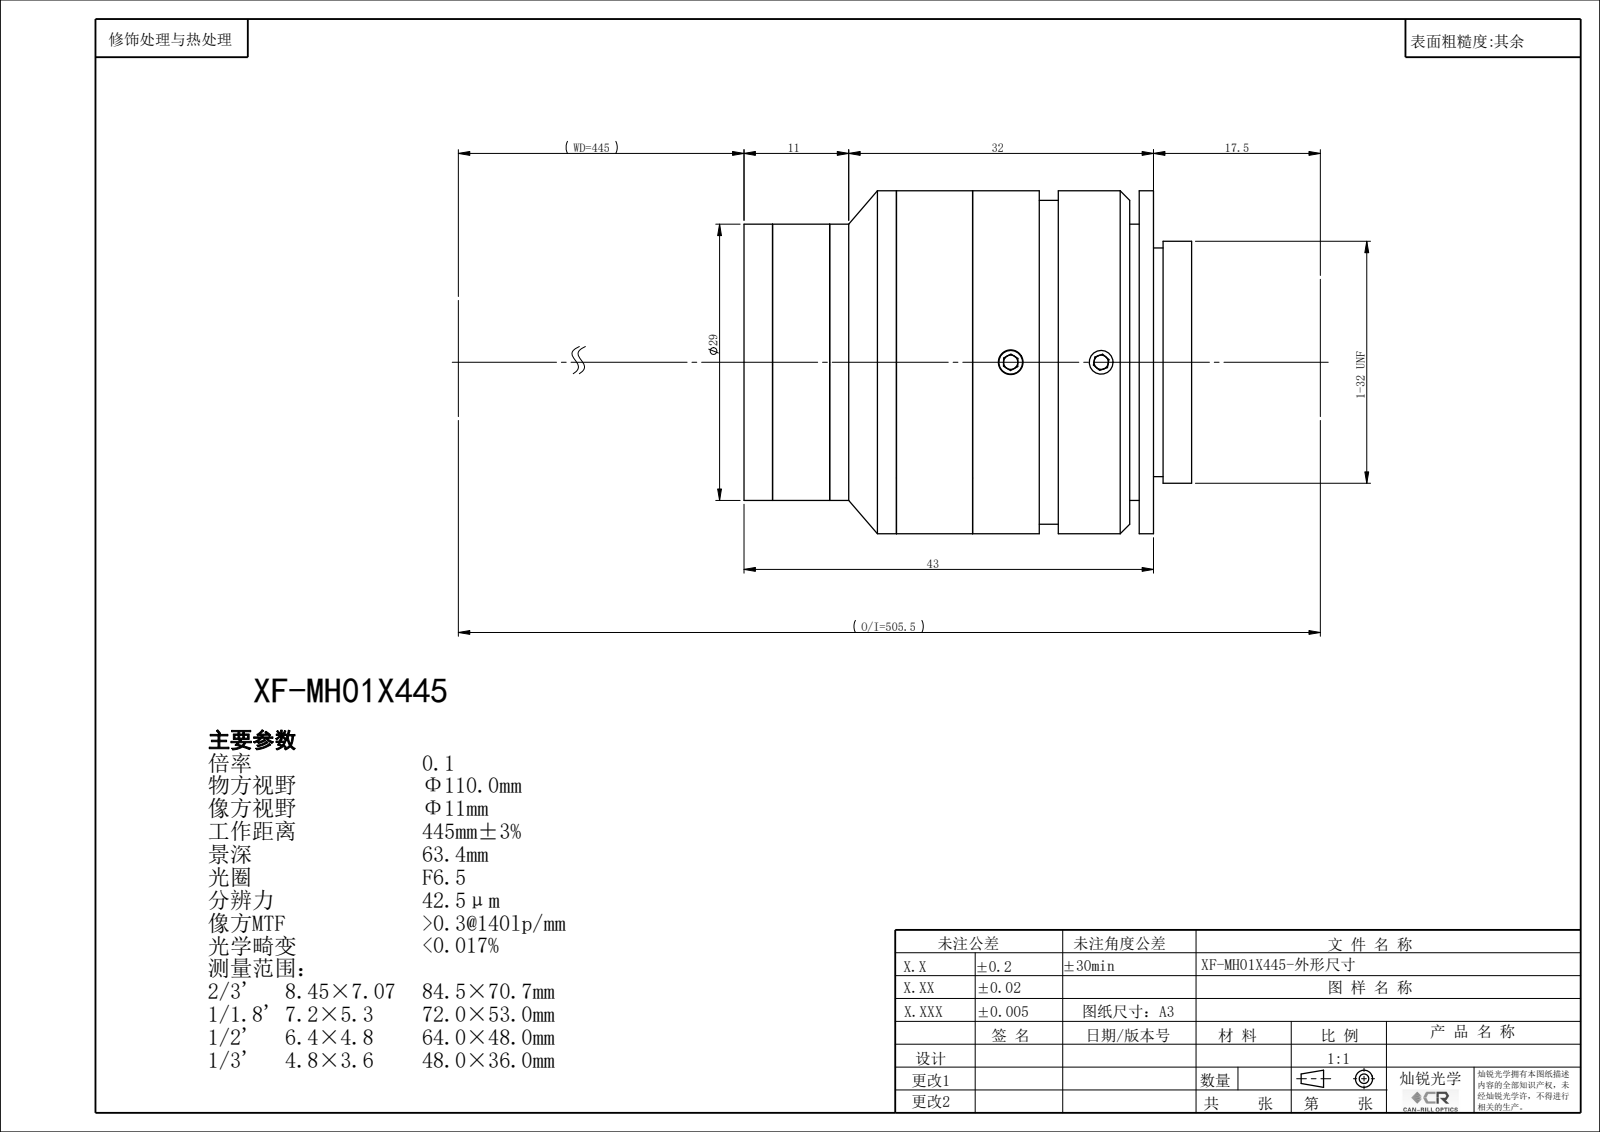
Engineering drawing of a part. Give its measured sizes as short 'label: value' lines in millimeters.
name: XF-MH01X445
written by: SolidWorks 2022 (CONFIG_CONTROL_DESIGN)
unit: mm
bodies: 0 solids, 132 faces (70 planar, 40 cylindrical, 22 other)
size: 47.02 × 36.05 × 36
holes: 3× ⌀2.5, 1× ⌀14, 1× ⌀22.4, 1× ⌀24, 1× ⌀24.9, 1× ⌀26.4, 1× ⌀27
bosses: 1× ⌀36, 1× ⌀34, 1× ⌀29, 1× ⌀25.4
face distances: 19, 20.22, 39.22, 14, 1.5, 1, 10.5, 37.72, 17.5, 12.22
